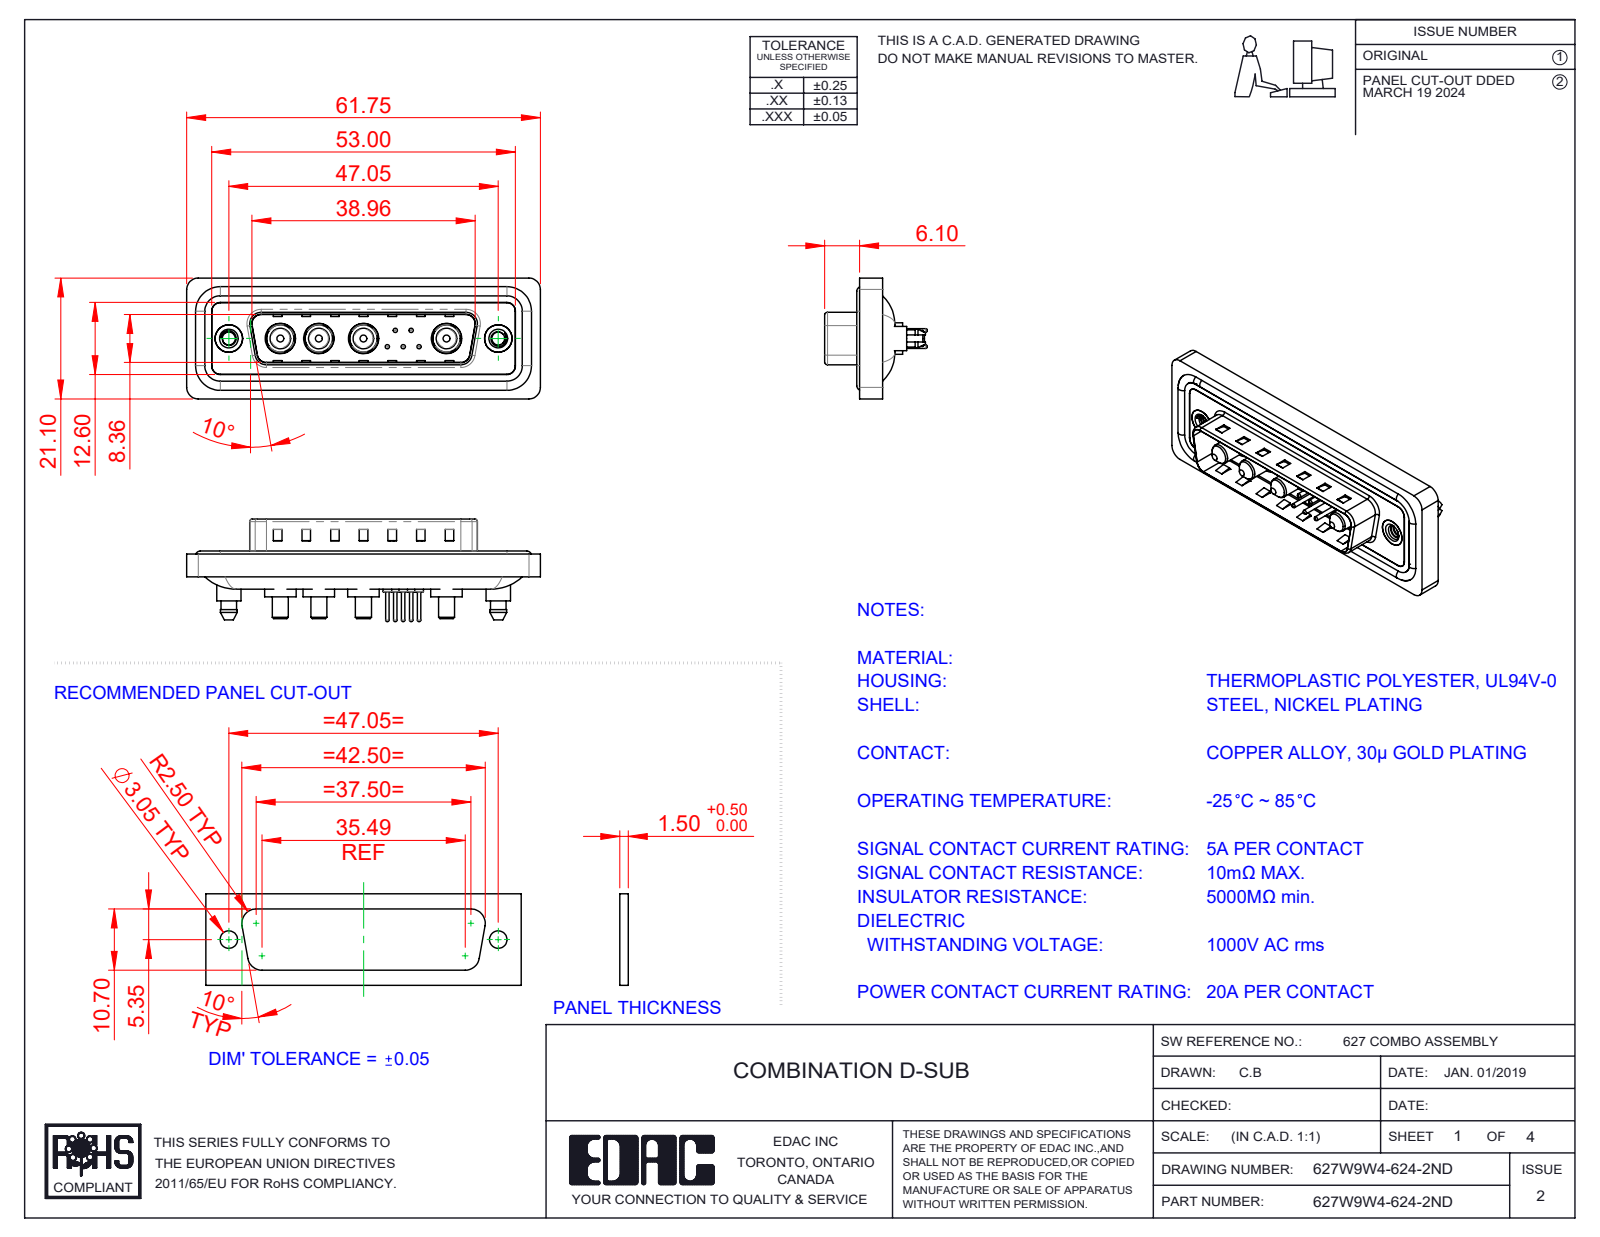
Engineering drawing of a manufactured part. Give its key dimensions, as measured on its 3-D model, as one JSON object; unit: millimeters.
{"part_name": "627Combo Waterproof Housing_25 Contacts; 627Combo Contact Row 2_24; 627W9W4-624-2ND; 627Combo Contact Row 1_24 (+6 more)", "step_written_by": "SolidWorks 2023 (CONFIG_CONTROL_DESIGN)", "units": "millimeters", "bodies": {"solids": 20, "faces": 882, "planar": 300, "cylindrical": 374, "other": 208}, "overall_size": [61.75, 21.1, 17.9], "volume_mm3": 7539, "surface_area_mm2": 12172, "round_holes": [[0.75, 5], [1.6, 5], [2, 5], [4.85, 4], [5.3, 4], [2.26, 2], [4, 2], [4.8, 2], [5, 2]], "round_bosses_or_shafts": [[1.5, 5], [0.6, 5], [5.5, 4], [5.2, 4], [4.75, 4], [3.75, 4], [3.6, 4], [2.8, 4]], "partial_cylinders_radius": [[1.5, 24], [2, 18], [1.6, 10], [0.5, 8], [0.25, 4], [0.6, 4], [0.65, 4], [0.9, 4]], "face_to_face_distances": [0.4, 1.5, 1.1, 0.5, 3.1, 1.6, 2.9, 0.82, 9.58, 5.65], "hole_center_spacings": [3.16, 2.77, 5.04, 14.51, 2.78, 4.4, 4.41, 5]}
